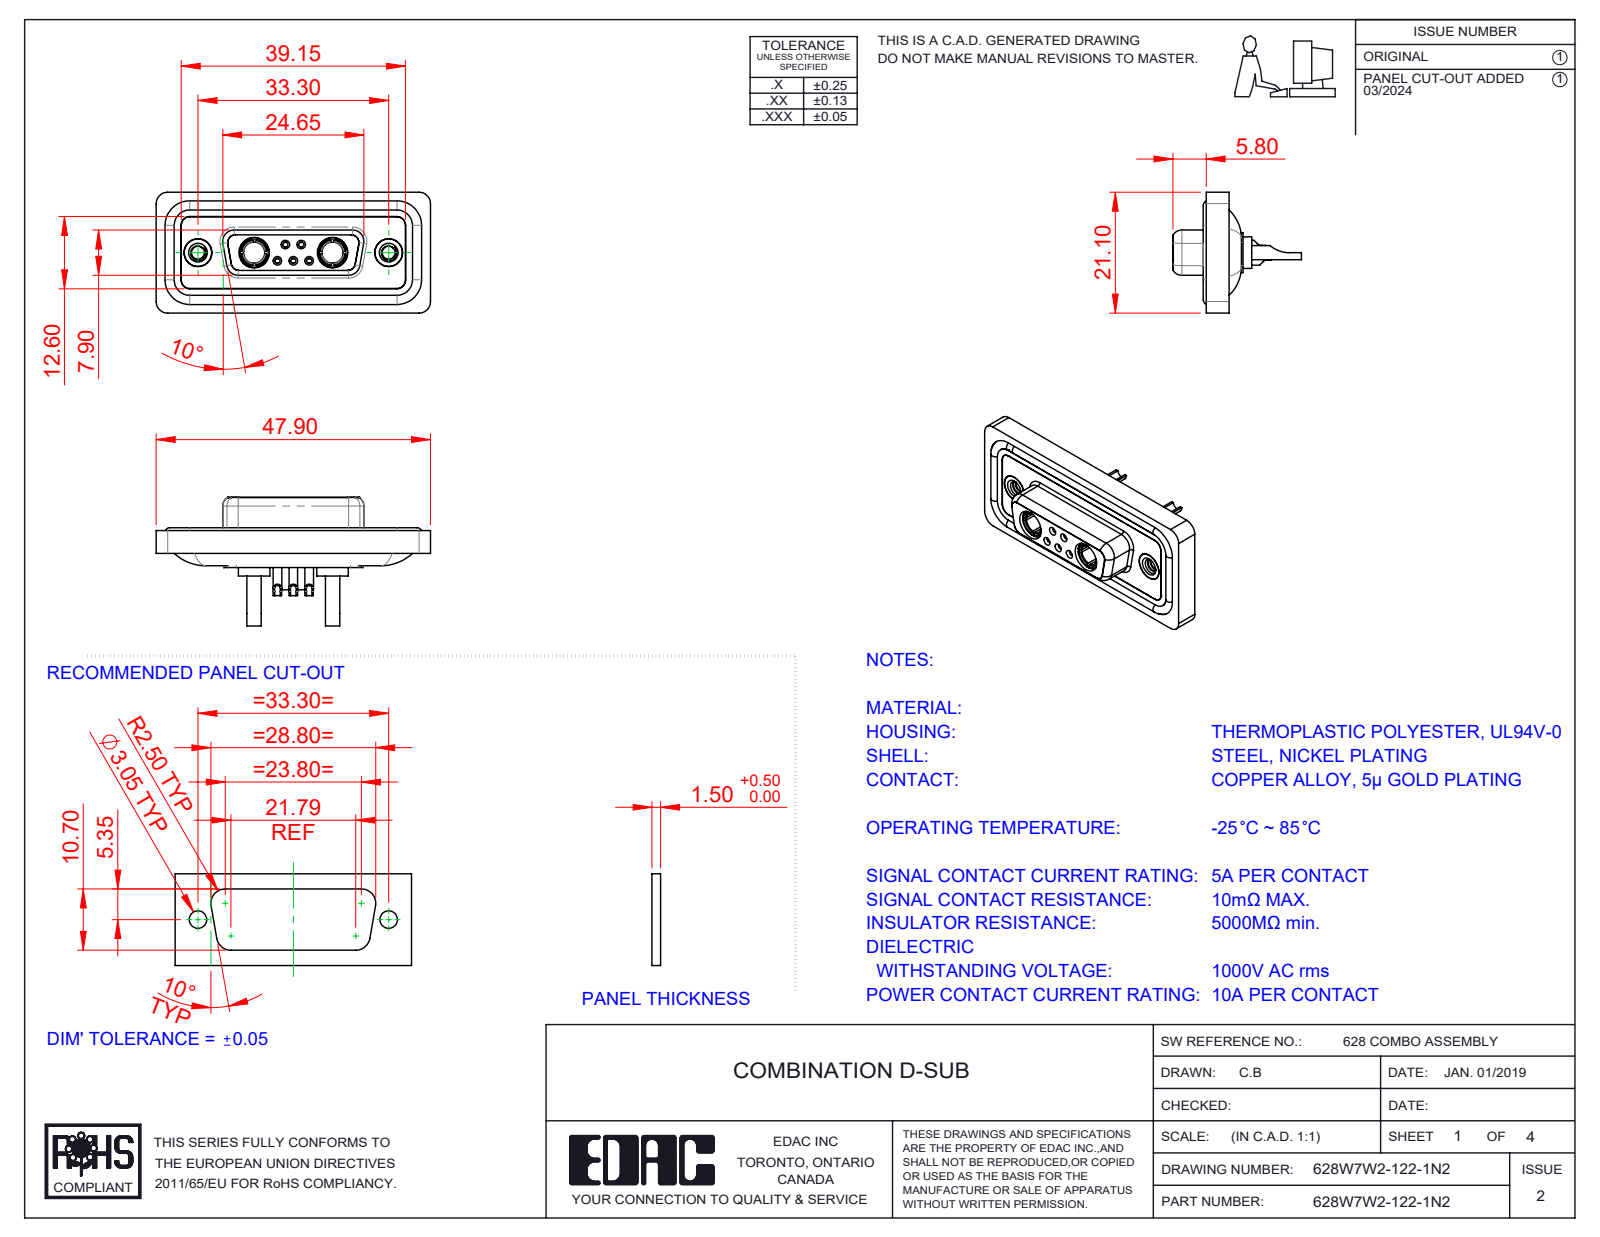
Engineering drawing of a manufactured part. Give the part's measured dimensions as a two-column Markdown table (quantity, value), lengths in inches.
| quantity | value |
| --- | --- |
| part name | 628Combo Shell Front_15 Contacts; 628Combo Housing_7W2; 628Combo Threaded Rivet_2; 628Combo Shell Rear_15 Contacts (+5 more) |
| STEP written by | SolidWorks 2023 (CONFIG_CONTROL_DESIGN) |
| units | inches |
| bodies | 16 solids, 819 faces (252 planar, 345 cylindrical, 222 other) |
| overall size | 1.886 × 0.884 × 0.831 |
| volume | 0.371 in³ |
| surface area | 15.55 in² |
| round holes (diameter × count) | 0.035 × 5, 0.039 × 5, 0.043 × 5, 0.059 × 5, 0.079 × 5, 0.191 × 4, 0.063 × 3, 0.067 × 2, 0.067 × 2, 0.089 × 2, 0.146 × 2, 0.157 × 2 |
| round bosses / shafts (diameter × count) | 0.063 × 6, 0.087 × 5, 0.217 × 2, 0.205 × 2, 0.195 × 2, 0.195 × 2, 0.189 × 2, 0.187 × 2 |
| partial cylindrical surfaces (radius × count) | 0.059 × 22, 0.079 × 20, 0.053 × 12, 0.063 × 8, 0.039 × 6, 0.01 × 4, 0.02 × 4, 0.024 × 4 |
| main face-to-face distances | 0.016, 0.071, 0.063, 0.02, 0.114, 0.043, 0.293, 0.222, 0.26, 0.278 |
| hole center spacings | 0.124, 0.109, 0.386, 0.925, 0.17, 0.17, 0.198, 0.198 |
